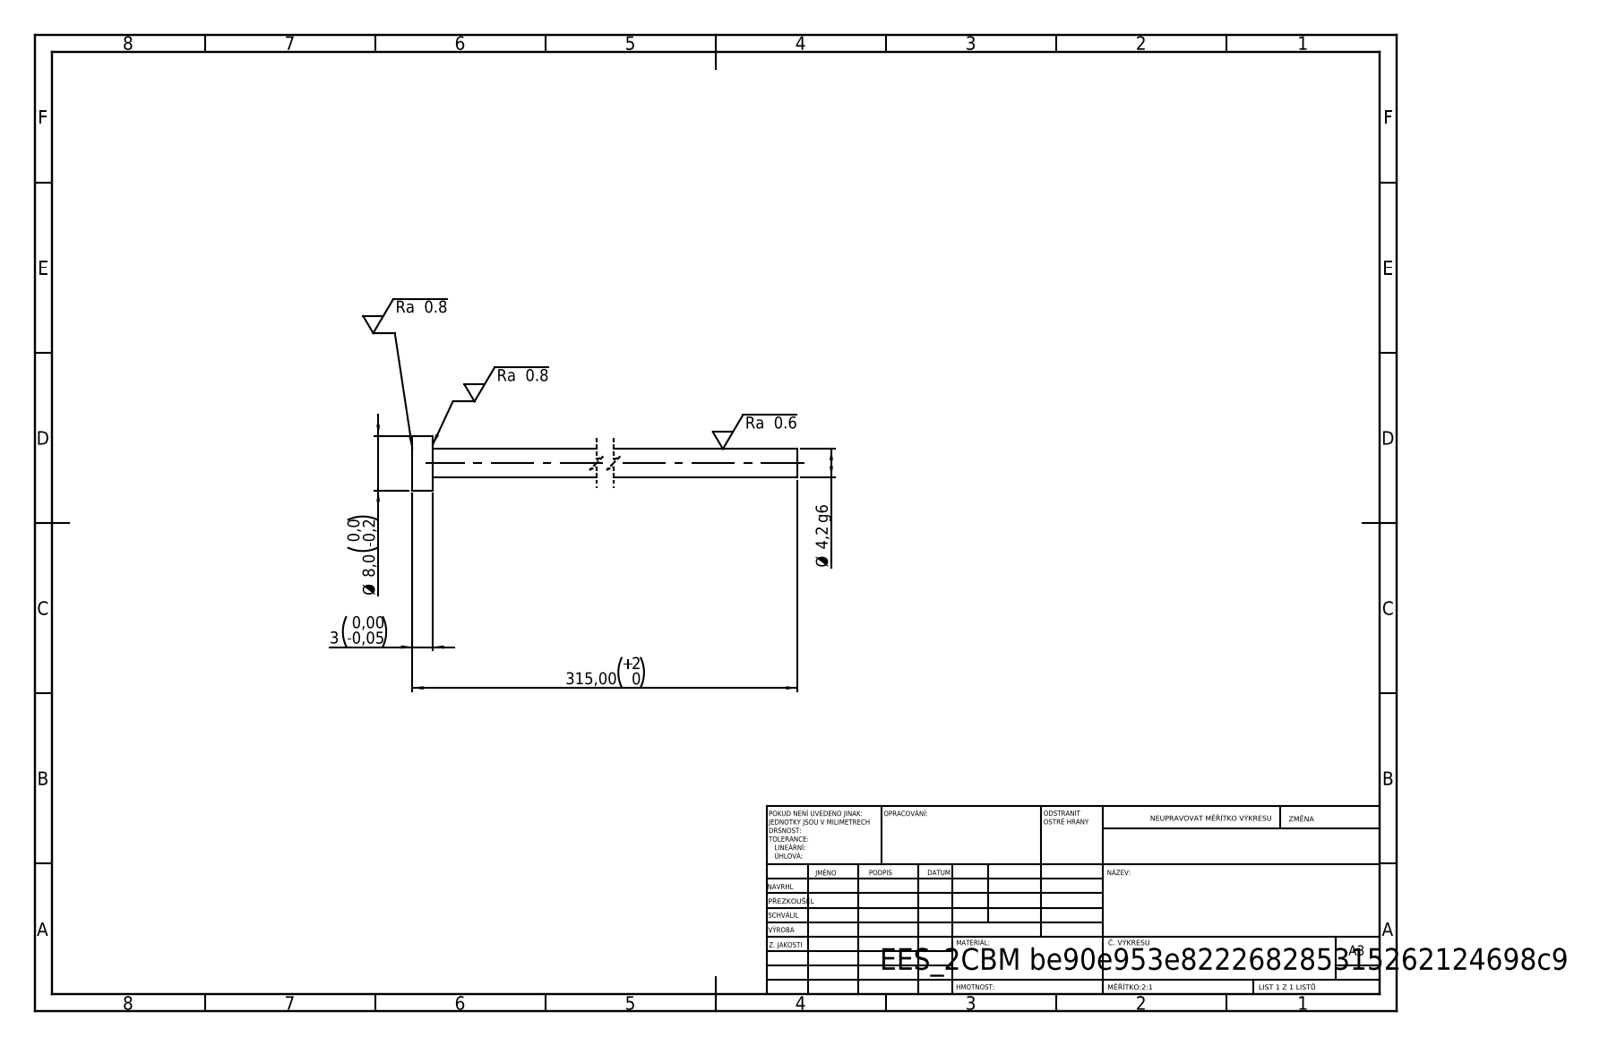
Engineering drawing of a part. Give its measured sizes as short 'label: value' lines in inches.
written by: SolidWorks 2019 (CONFIG_CONTROL_DESIGN)
unit: in
bodies: 1 solid, 7 faces (3 planar, 4 cylindrical, 0 other)
size: 12.402 × 0.315 × 0.315
volume: 0.273 in³; area: 6.654 in²
bosses: 1× ⌀0.315, 1× ⌀0.165
face distances: 0.118, 12.402, 12.283
